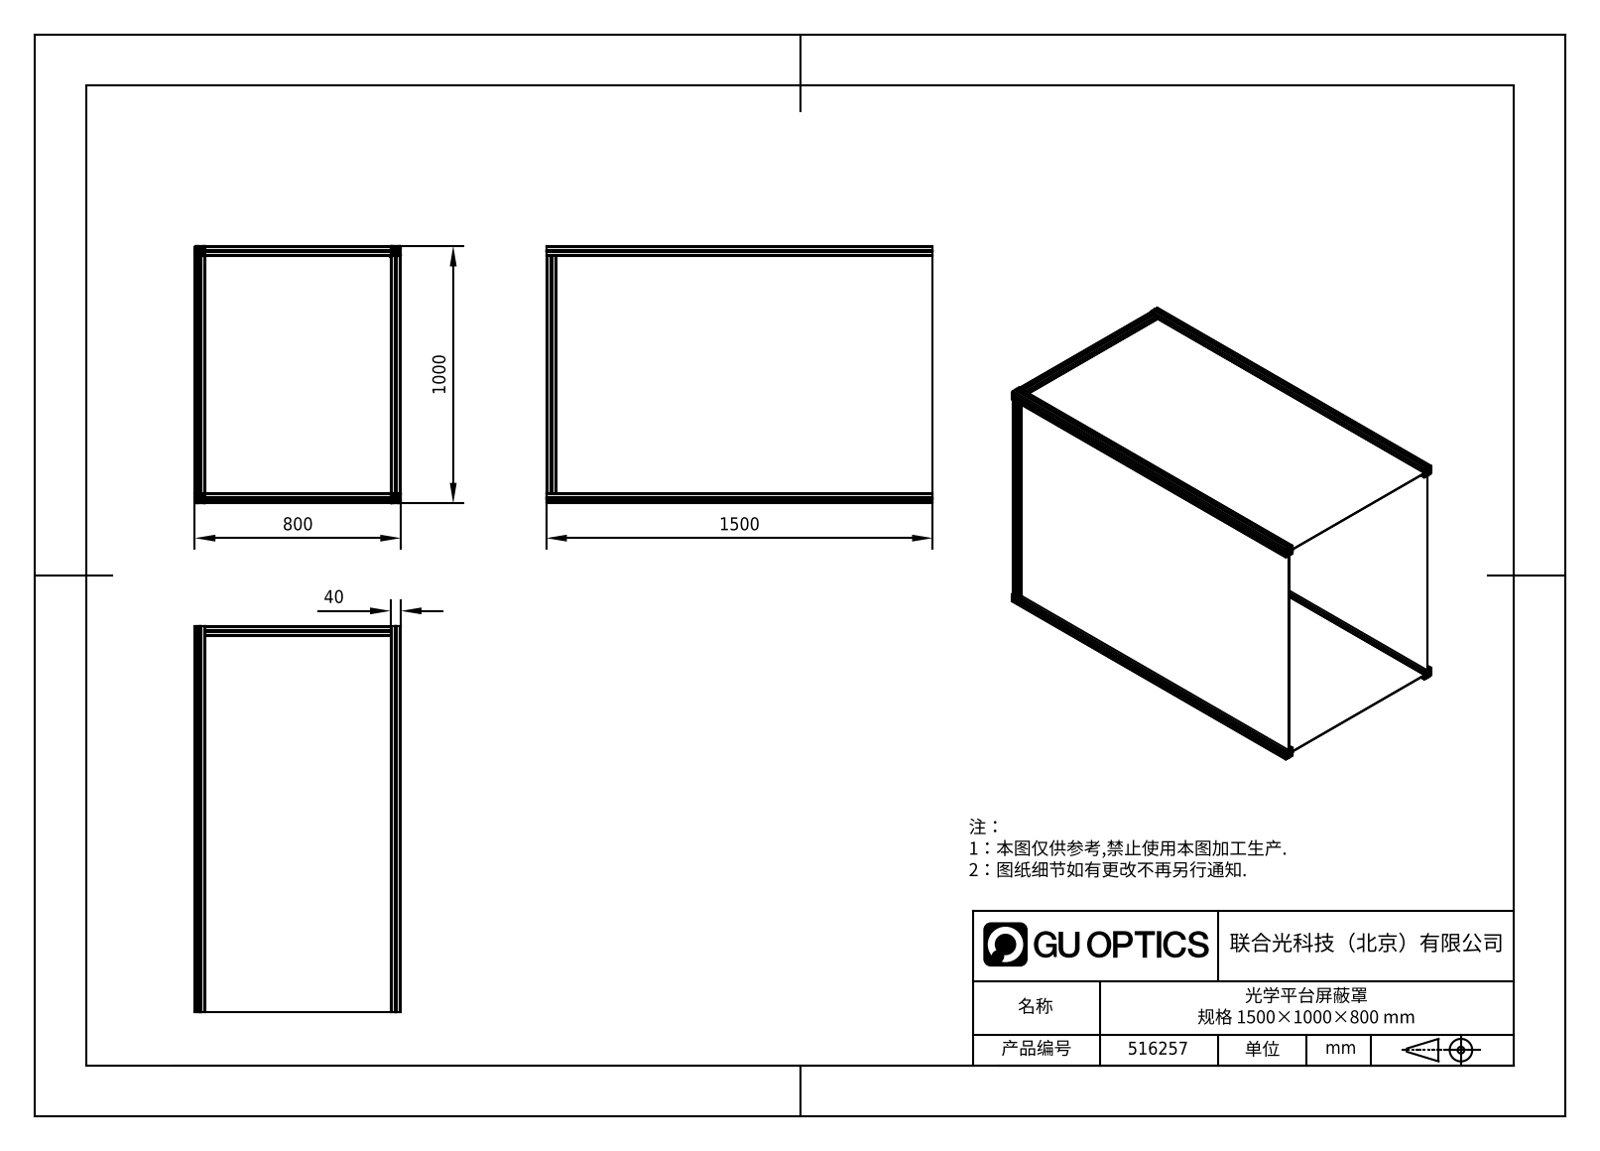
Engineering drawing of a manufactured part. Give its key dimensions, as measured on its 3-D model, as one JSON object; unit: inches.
{"part_name": "光学平台屏蔽罩边框_720; 光学平台屏蔽罩边框_1500; 光学平台屏蔽罩边框_920; 516257 (+3 more)", "step_written_by": "SolidWorks 2020 (CONFIG_CONTROL_DESIGN)", "units": "inches", "bodies": {"solids": 13, "faces": 1230, "planar": 950, "cylindrical": 280, "other": 0}, "overall_size": [59.055, 39.37, 31.496], "volume_in3": 1031, "surface_area_in2": 24740, "partial_cylinders_radius": [[0.02, 64], [0.039, 64], [0.03, 32], [0.098, 32], [0.177, 32], [0.134, 8]], "face_to_face_distances": [0.079, 29.921, 37.795, 30, 29.843, 37.874, 37.717, 0.748, 0.827, 0.323]}
